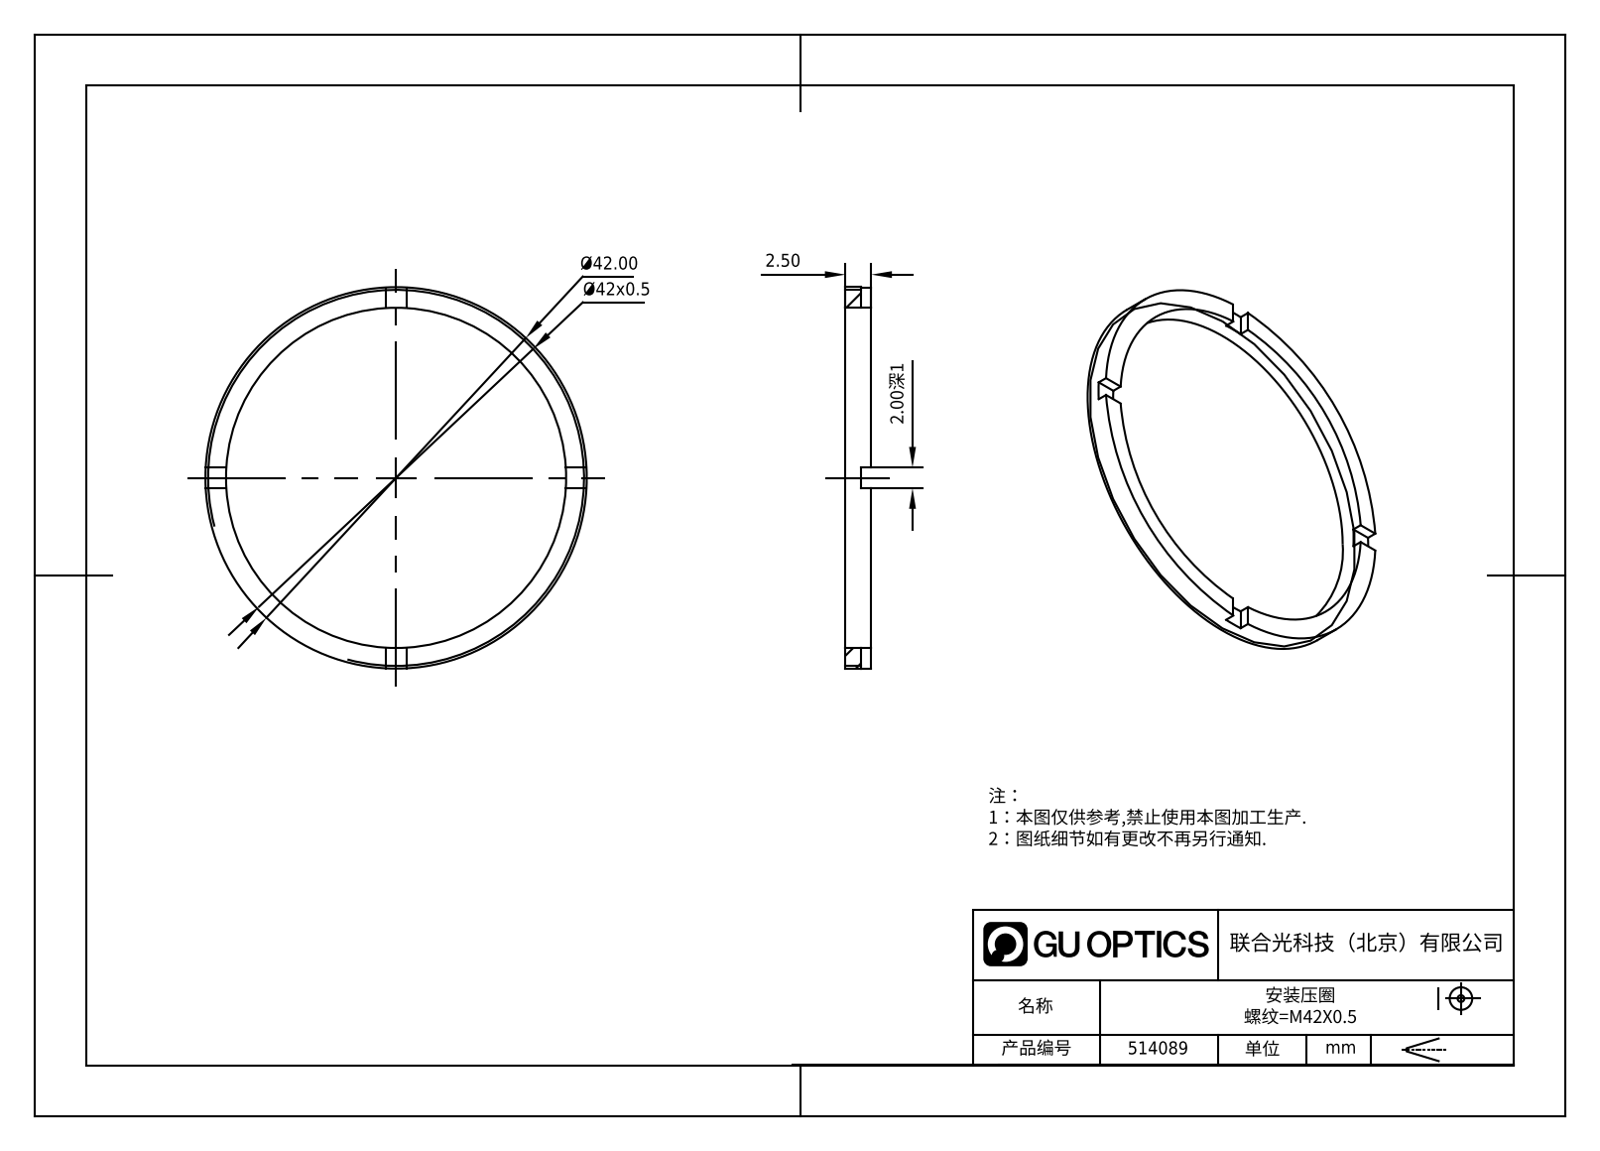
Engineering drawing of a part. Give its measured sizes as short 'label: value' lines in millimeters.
name: 514089
written by: SolidWorks 2020 (CONFIG_CONTROL_DESIGN)
unit: mm
bodies: 1 solid, 21 faces (17 planar, 4 cylindrical, 0 other)
size: 42 × 42 × 2.5
volume: 612 mm³; area: 1 131 mm²
holes: 1× ⌀38
bosses: 1× ⌀42
face distances: 2.5, 1.5, 1, 2
